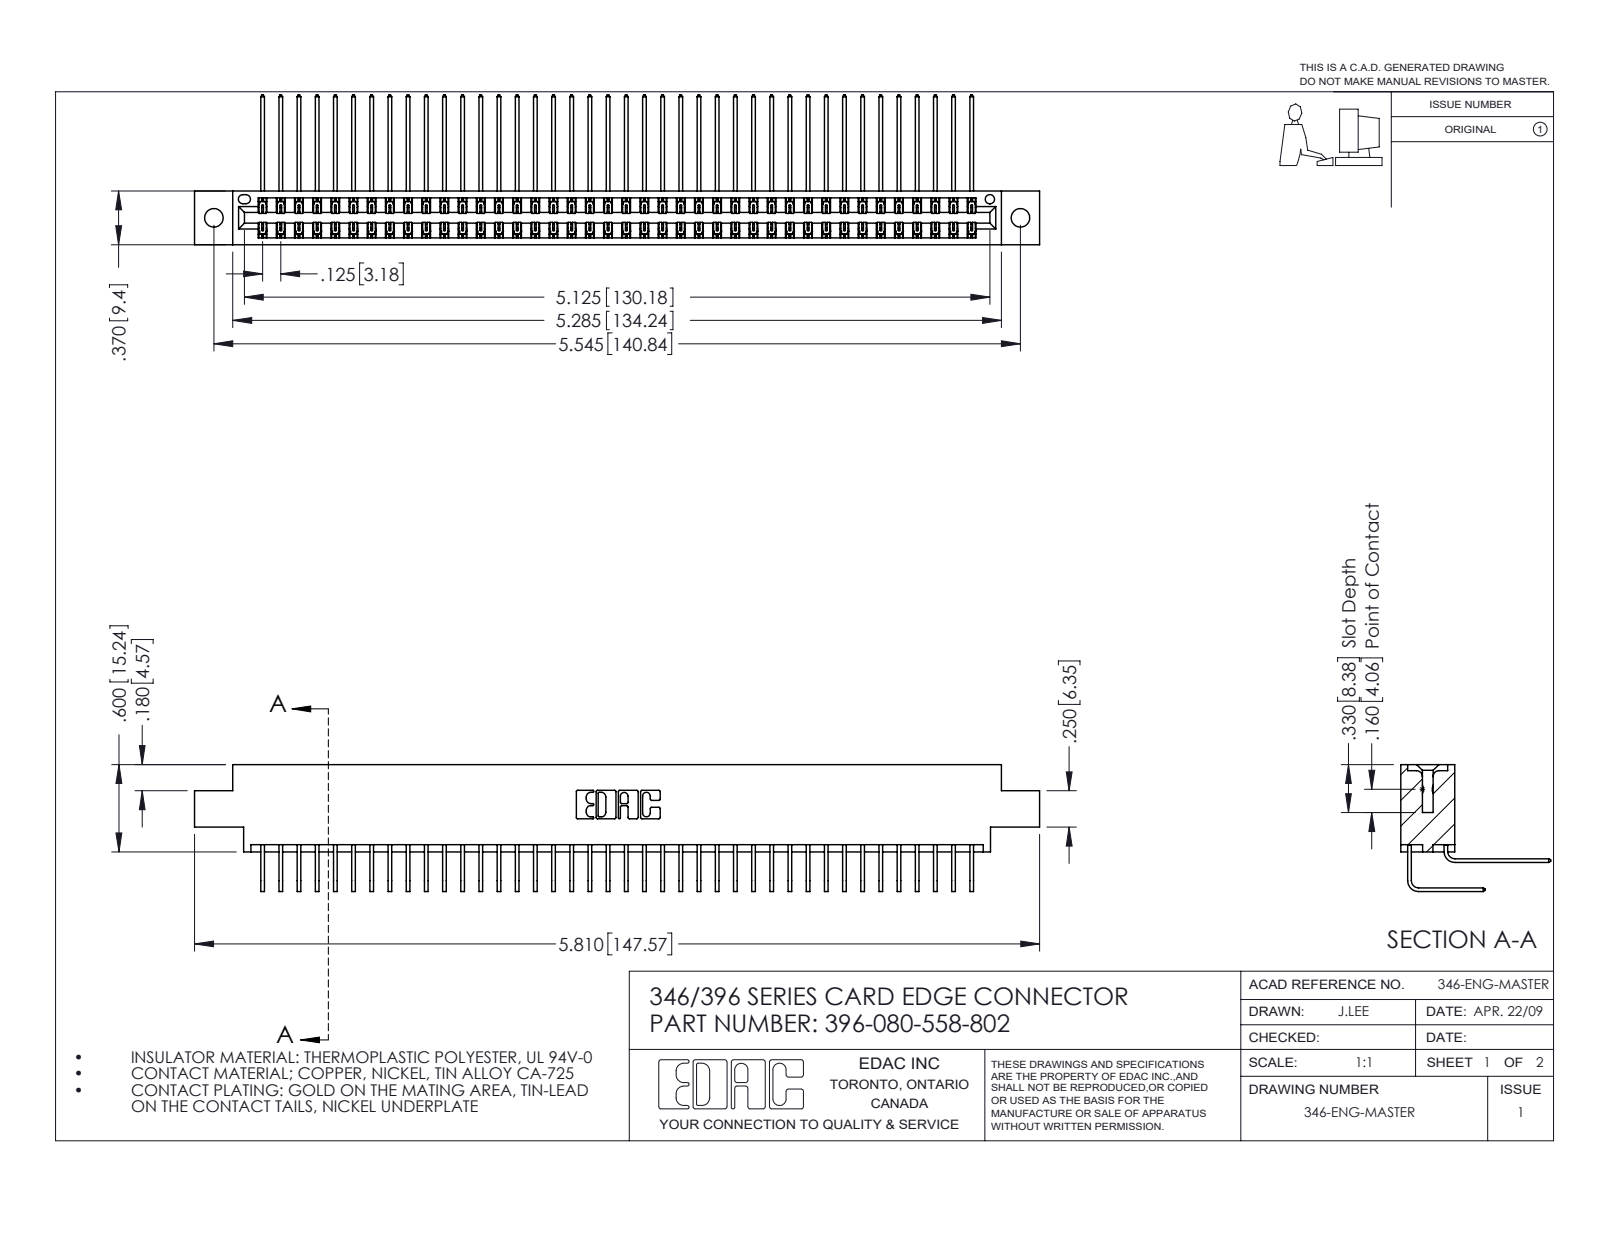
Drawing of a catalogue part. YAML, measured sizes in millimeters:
part_name: "345-292-001_558 Tail - 2; 346 Part_0.170 Offset - 0.128 Dia; 345-292-001_558 559 Tail - 1; 396-080-558-802"
step_written_by: "SolidWorks 2016 (CONFIG_CONTROL_DESIGN)"
units: millimeters
bodies: {solids: 81, faces: 4446, planar: 3040, cylindrical: 1406, other: 0}
overall_size: [147.6, 26.2, 22.2]
volume: 14700
surface_area: 22230
round_holes:
  - {diameter: 3.3, count: 2}
  - {diameter: 1.6, count: 1}
partial_cylinders:
  - {radius: 0.2, count: 120}
  - {radius: 0.3, count: 22}
  - {radius: 0.2, count: 6}
  - {radius: 0.8, count: 6}
  - {radius: 0.7, count: 3}
  - {radius: 0.4, count: 2}
  - {radius: 0.6, count: 2}
  - {radius: 0.6, count: 2}
face_to_face_distances: [8.2, 1.2, 0.6, 9.4, 6.4, 7.6, 1.8, 7, 3.8, 5.6]
hole_center_spacings: [6.2, 135.5, 140.8]
